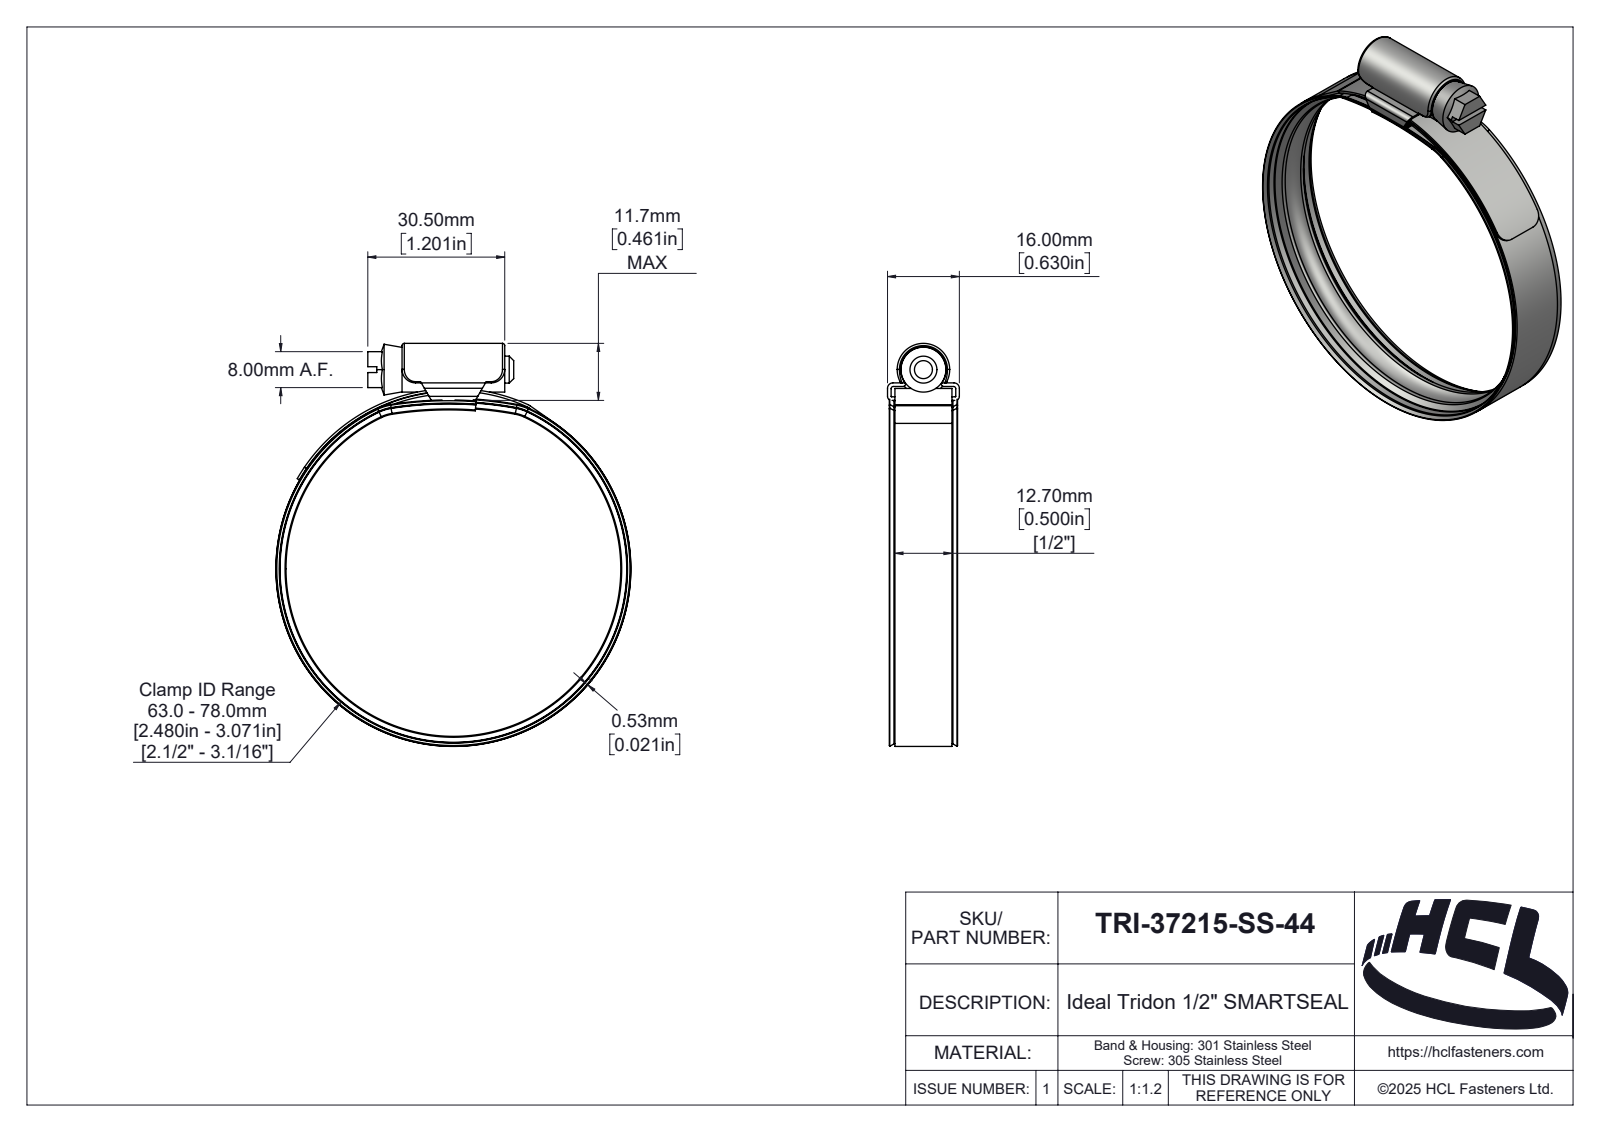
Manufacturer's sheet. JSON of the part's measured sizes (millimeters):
{"part_name": "TRI-37215-SS-44", "step_written_by": "SolidWorks 2025 (AUTOMOTIVE_DESIGN)", "units": "millimeters", "bodies": {"solids": 4, "faces": 418, "planar": 42, "cylindrical": 119, "other": 257}, "overall_size": [89.73, 79.06, 16], "volume_mm3": 5847, "surface_area_mm2": 19192, "round_holes": [[77.4, 1], [78, 1]], "round_bosses_or_shafts": [[79.06, 1], [77.8, 1], [10, 1], [6, 1]], "partial_cylinders_radius": [[0.5, 6], [3, 4], [0.1, 2], [0.9, 2], [1.2, 2], [9.9, 2], [10.1, 2], [0.46, 1]], "face_to_face_distances": [0.8, 12.7, 3.1, 0.53, 2.3, 30.5, 3.9, 1.65, 14.35, 15.2]}
